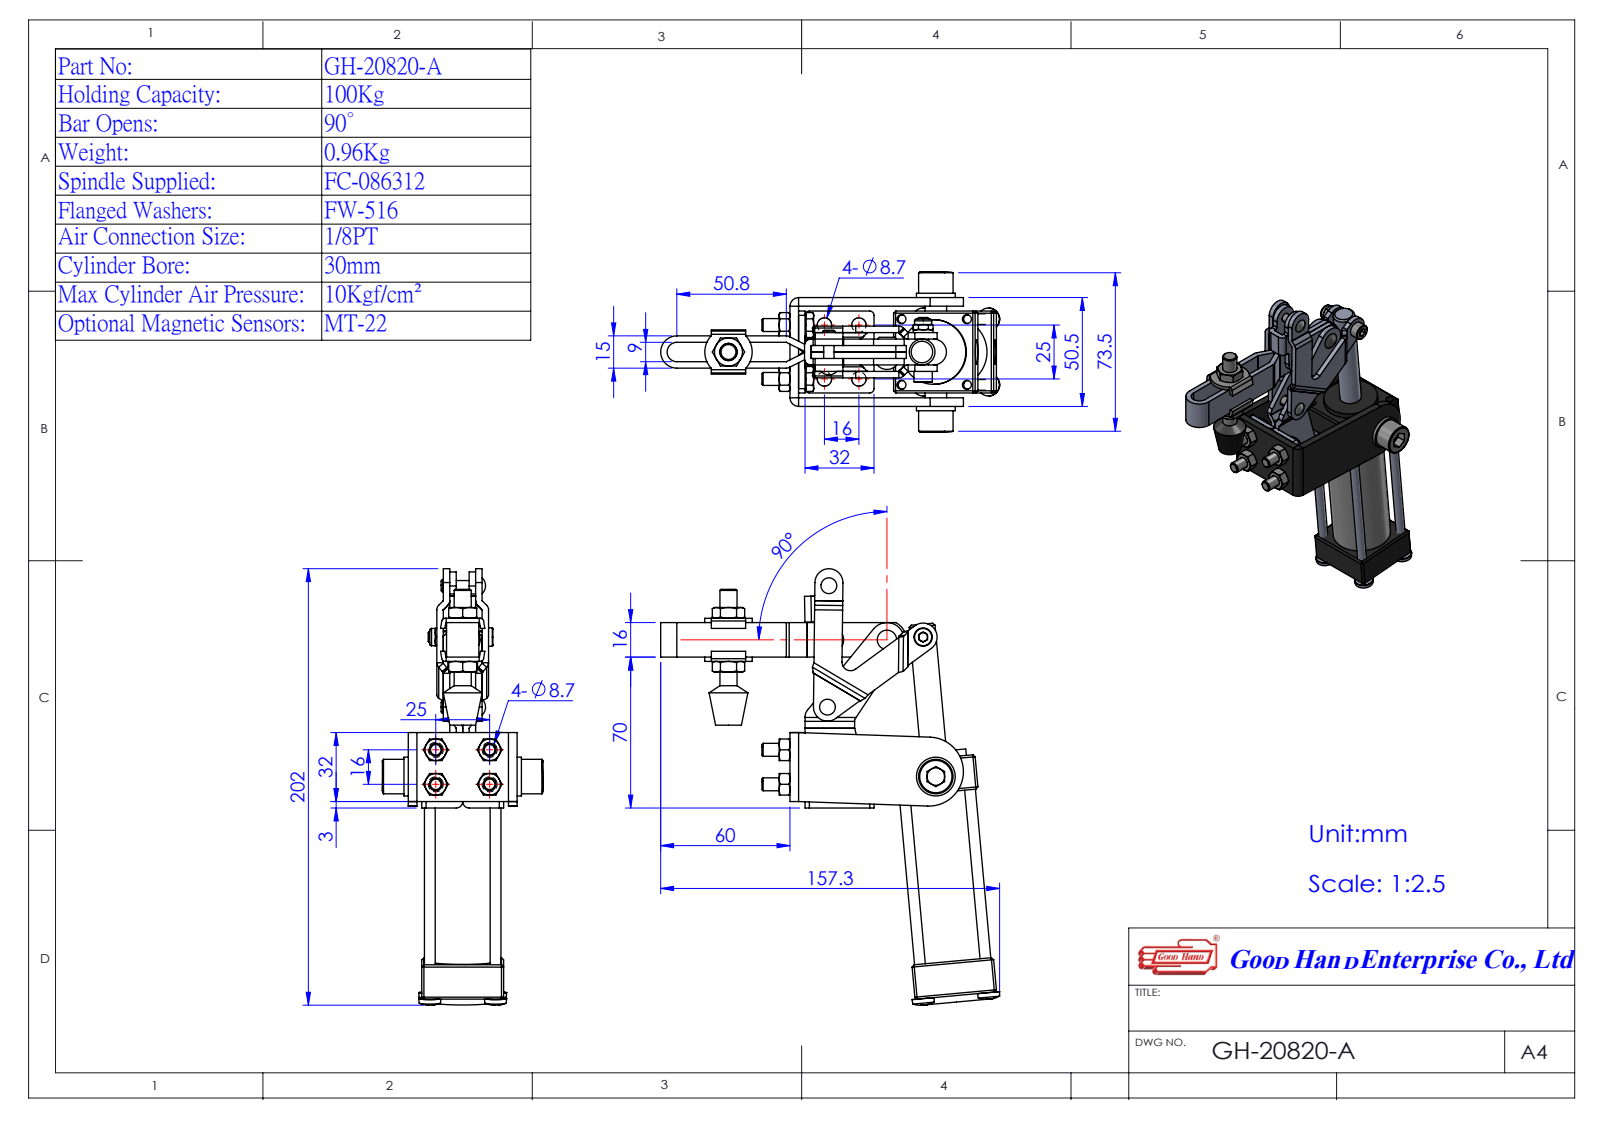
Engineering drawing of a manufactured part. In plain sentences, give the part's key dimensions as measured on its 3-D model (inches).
The part is named "Group6^GH-20820-A(簡化)-1; Group8^GH-20820-A(簡化)-1; Hexagon Nut_3_JIS-7^GH-20820-A(簡化)-1; 20820A-CYLINDER-1^GH-20820-A(簡化)-1 (+4 more)". Its 3-D file was written by "SolidWorks 2016 (AUTOMOTIVE_DESIGN)". It is 8 solids with 1539 faces: 545 planar, 394 cylindrical and 600 other. Overall it measures 7.918 by 6.193 by 2.639 inches. Its volume is 9.337 cubic inches and its surface area 146.7 square inches. Round holes: 8 of diameter 0.165, 4 of diameter 0.264, 3 of diameter 0.197, 3 of diameter 0.252, 2 of diameter 0.332, 1 of diameter 0.157, 1 of diameter 0.236, 1 of diameter 0.257, 1 of diameter 0.307, 1 of diameter 0.472, 1 of diameter 0.63, 1 of diameter 1.181. Round bosses or shafts: 5 of diameter 0.197, 4 of diameter 0.406, 4 of diameter 0.394, 3 of diameter 1.181, 3 of diameter 0.236, 2 of diameter 0.315, 2 of diameter 0.248, 2 of diameter 0.228. Partial cylindrical surfaces (rounded edges, fillets, slot ends): 20 of radius 0.119, 8 of radius 0.079, 6 of radius 0.118, 3 of radius 0.256, 2 of radius 0.039, 2 of radius 0.158, 2 of radius 0.252, 1 of radius 0.157. The main face-to-face distances are 0.118, 0.236, 0.354, 0.157, 0.472, 0.591, 0.719, 0.955, 0.876, 1.112. The hole center spacings are 0.849, 1.201, 0.849, 1.201, 1.698, 0.63, 0.85, 0.984.
